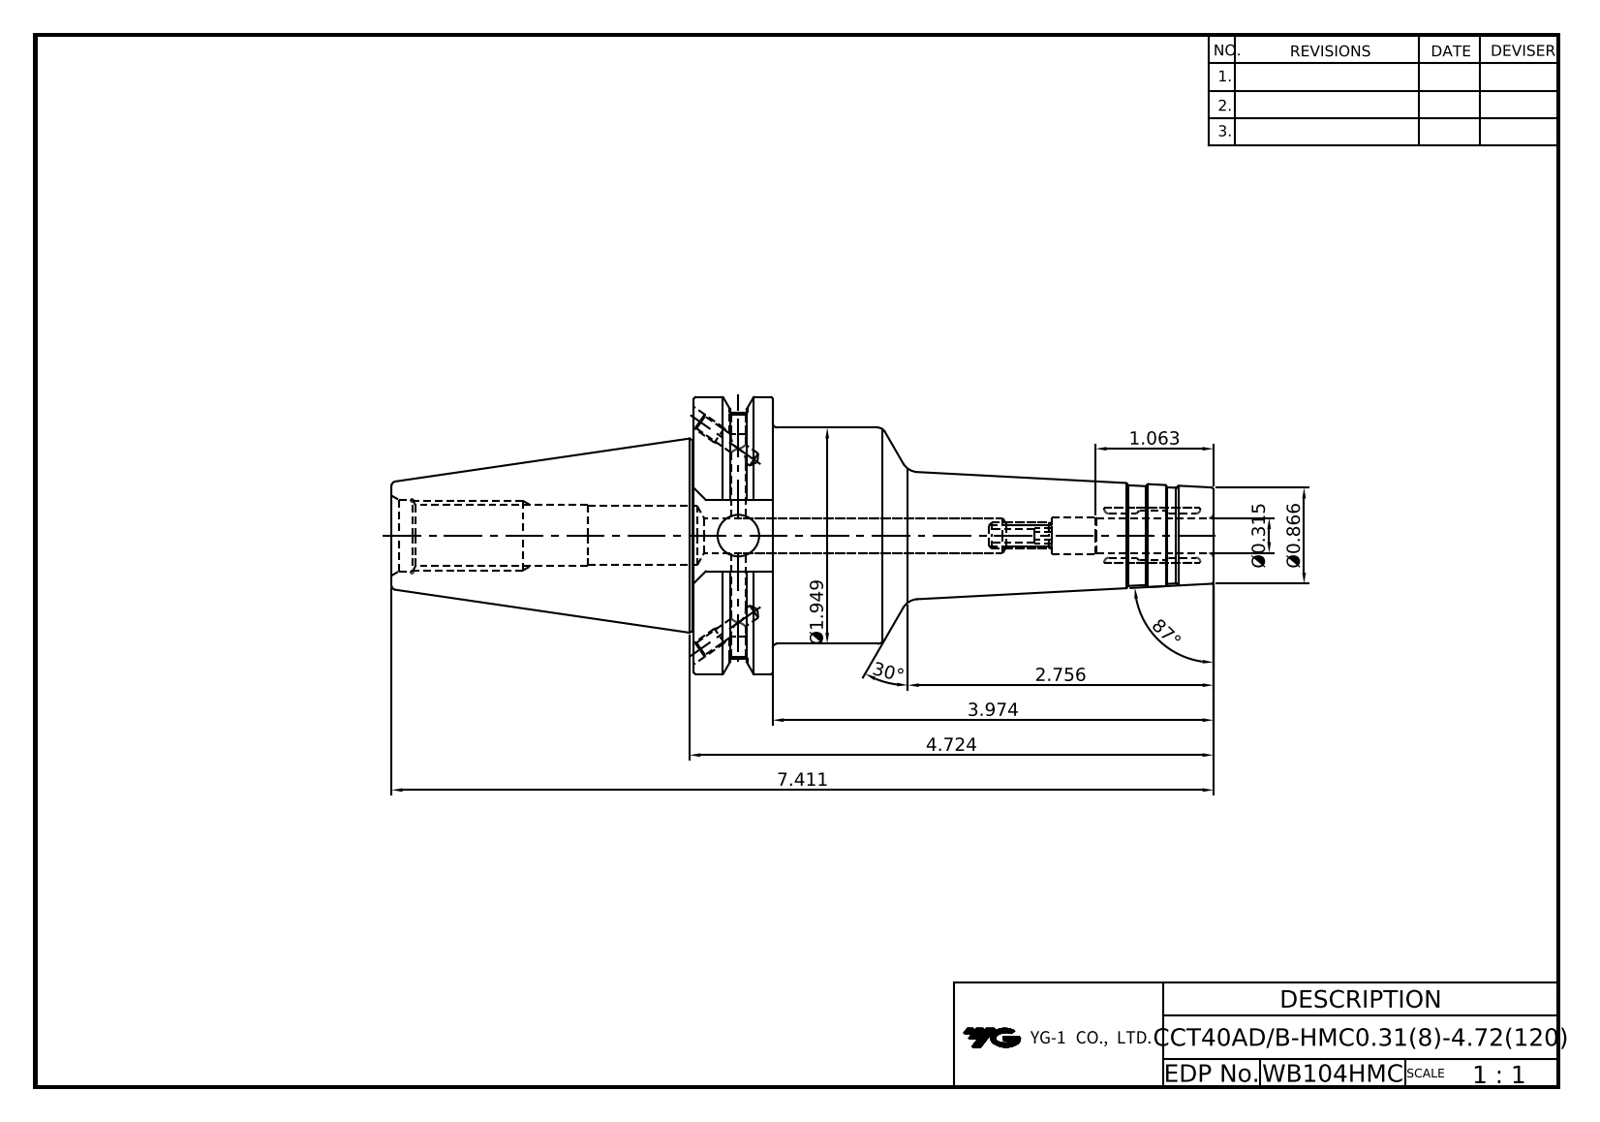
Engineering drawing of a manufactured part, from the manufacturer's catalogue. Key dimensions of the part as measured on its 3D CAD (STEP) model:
Part name (STEP PRODUCT): LO-CCT40ADB-HMC8-120
STEP written by: Autodesk Inventor 2020 (AUTOMOTIVE_DESIGN)
Units: millimetres
Bodies: 1 solid, 108 faces (35 planar, 31 cylindrical, 42 other)
Overall size (bounding box): 188.25 × 63.5 × 61.09
Volume: 192 025 mm³ · Surface area: 32 762 mm²
Round holes (diameter × count): ⌀3.24 ×4, ⌀4 ×2, ⌀4.2 ×2, ⌀4.92 ×1, ⌀8 ×1, ⌀8.6 ×1, ⌀9.53 ×1, ⌀13 ×1, ⌀13.39 ×1, ⌀16.3 ×1
Round bosses / shafts (diameter × count): ⌀63.5 ×1, ⌀49.5 ×1, ⌀43.8 ×1
Partial cylindrical surfaces — rounded edges, fillets, slot ends (radius × count): R8.19 ×1, R28.15 ×1
Main face-to-face distances: 18.05, 119, 100.95, 47.6, 16.38, 69.25, 87.3, 188.25, 81.34, 12.09
